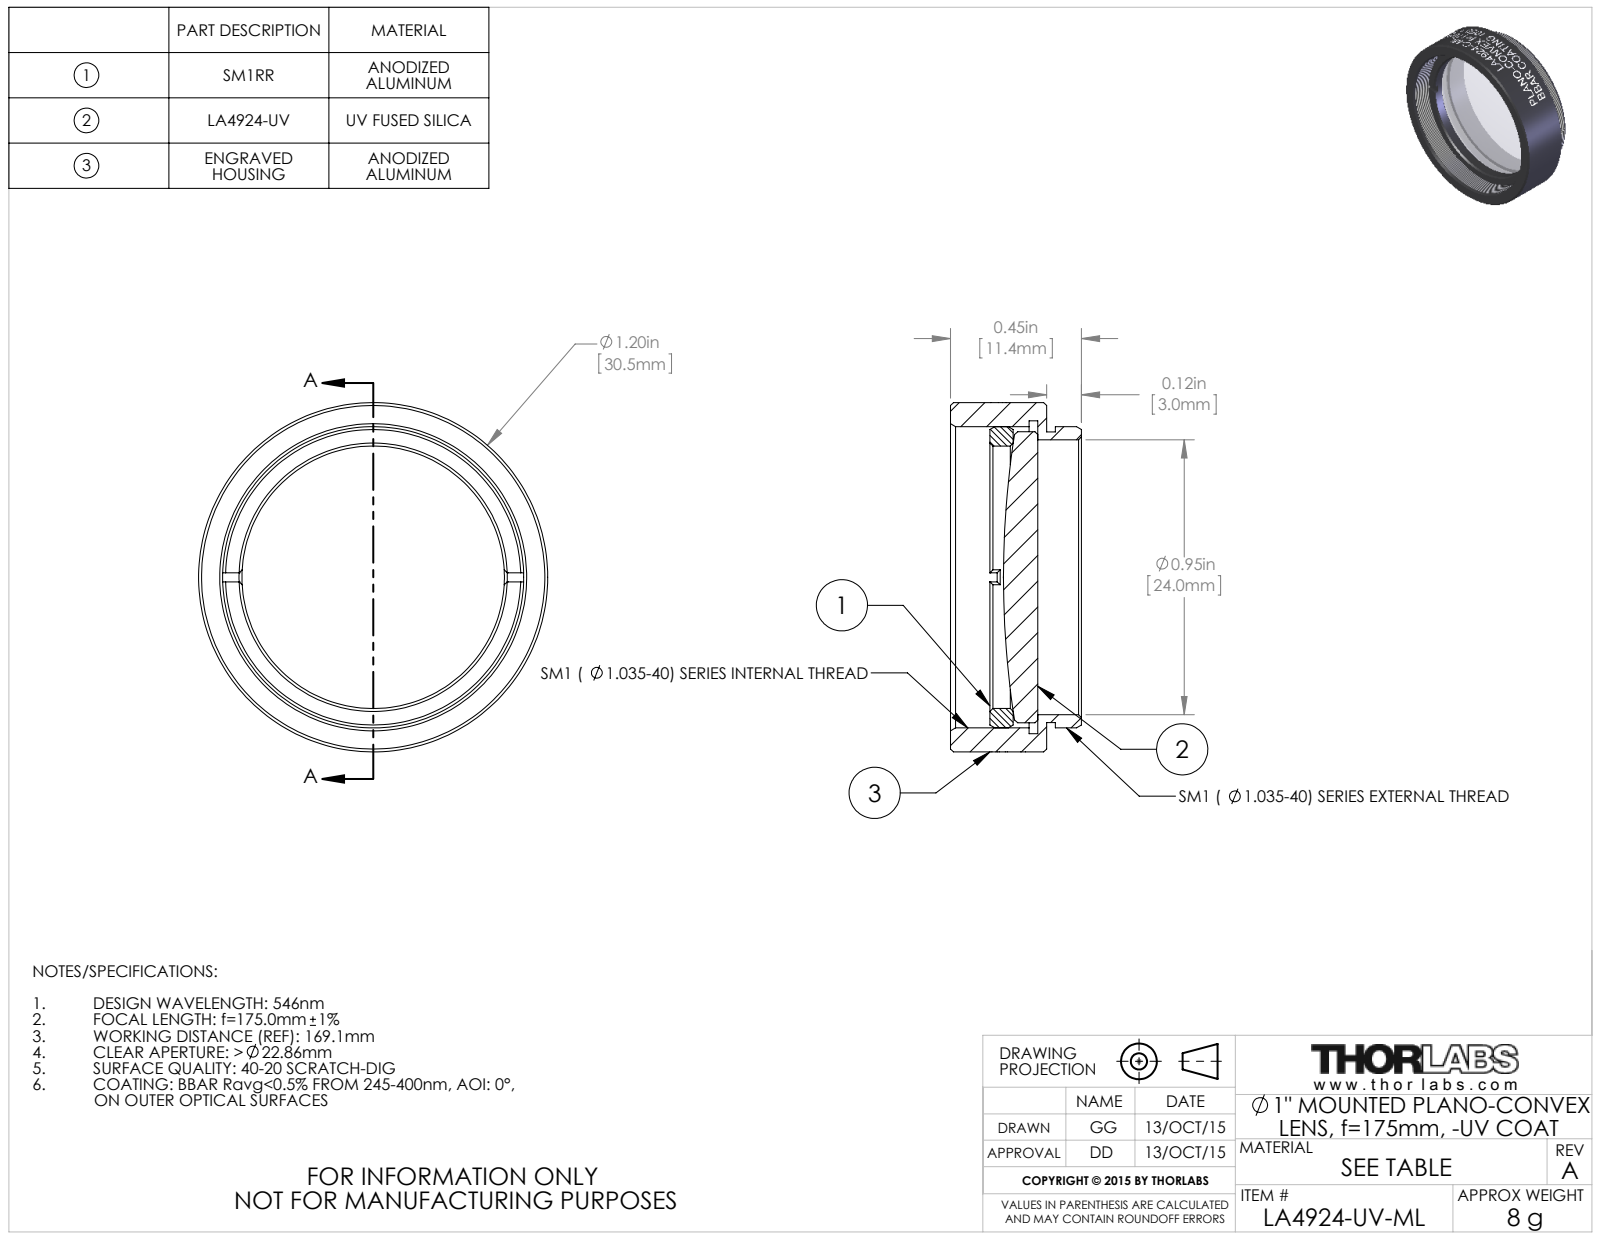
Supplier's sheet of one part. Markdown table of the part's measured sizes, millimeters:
| quantity | value |
| --- | --- |
| part name | TTN039449-E0W |
| STEP written by | SolidWorks 2014 (CONFIG_CONTROL_DESIGN) |
| units | millimeters |
| bodies | 3 solids, 160 faces (20 planar, 112 cylindrical, 28 other) |
| overall size | 30.48 × 30.48 × 11.43 |
| volume | 3 345 mm³ |
| surface area | 4 294 mm² |
| round holes (diameter × count) | 22.91 × 1, 24 × 1, 27.31 × 1 |
| round bosses / shafts (diameter × count) | 30.48 × 1, 26.29 × 1, 25.4 × 1, 25.37 × 1 |
| main face-to-face distances | 0.76, 8.38, 7.62, 2.92, 2.16, 5.46, 4.95, 4.19, 2.03, 3.43 |
